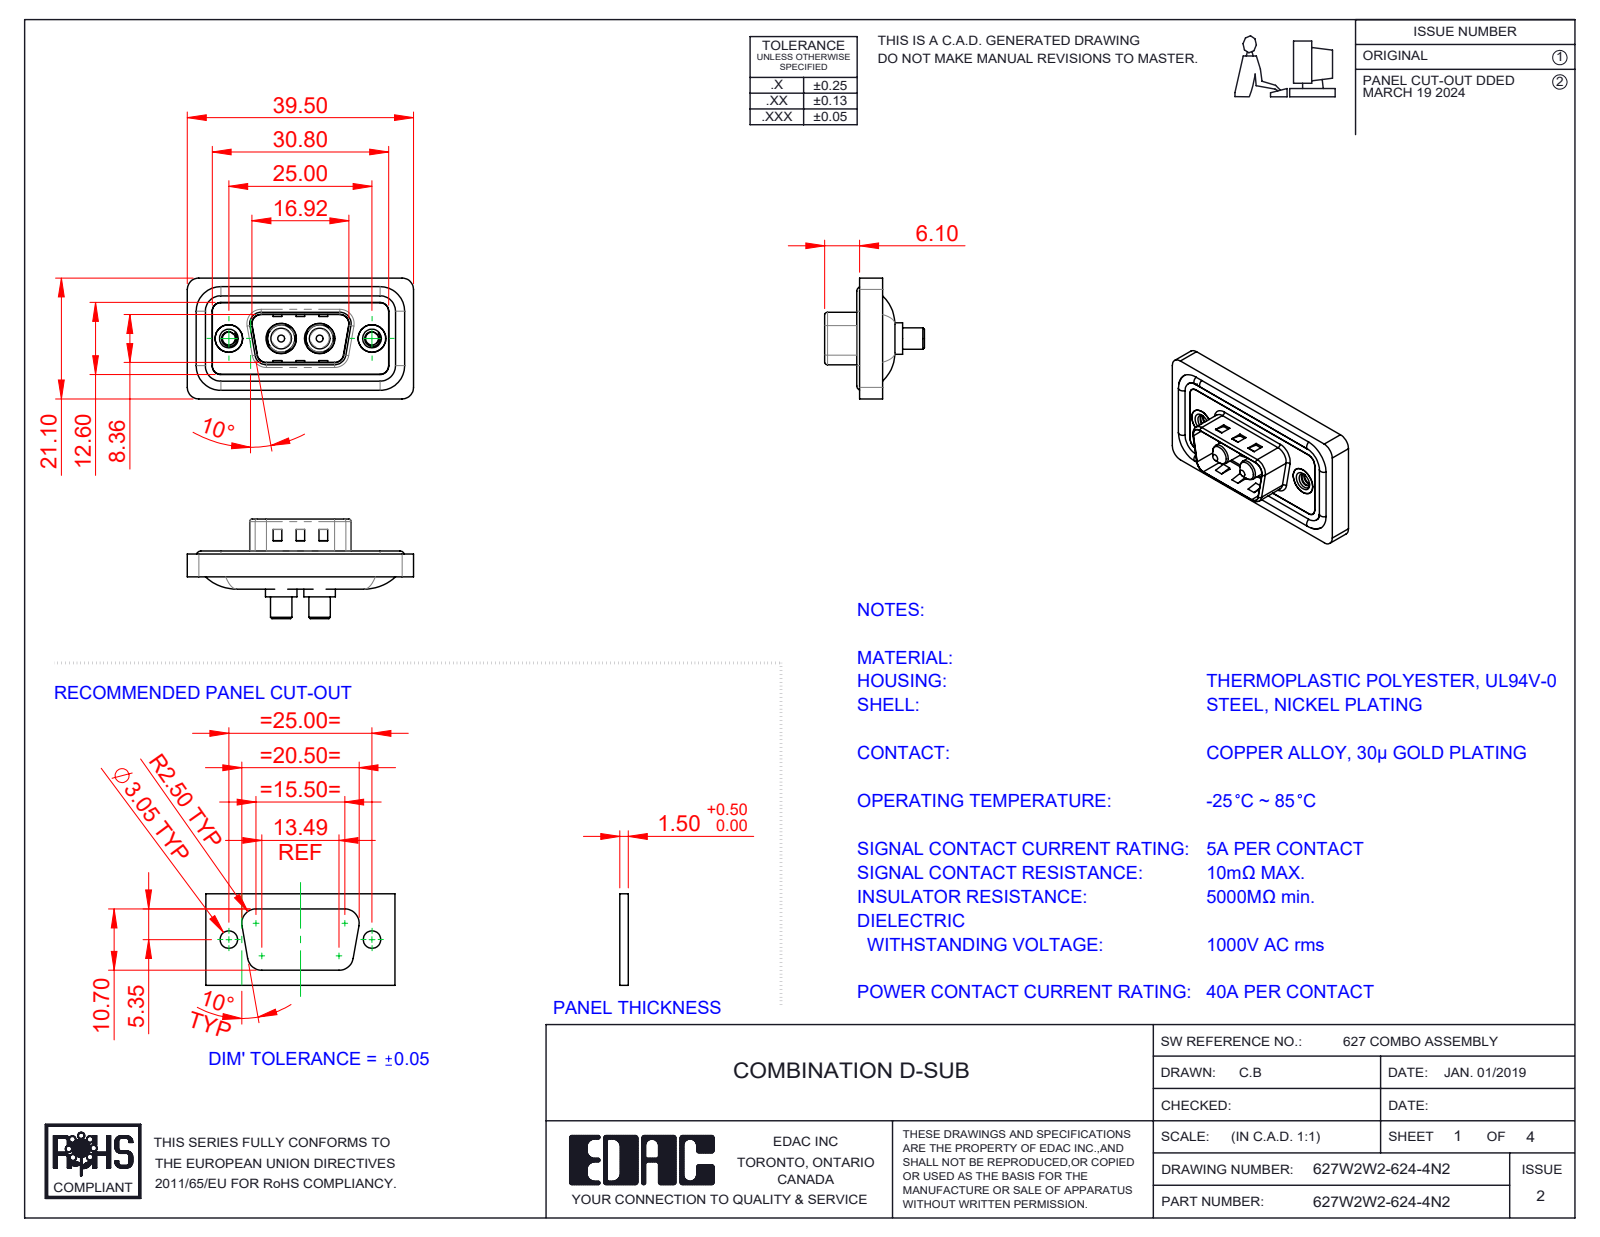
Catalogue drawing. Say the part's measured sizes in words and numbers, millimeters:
The part is named "Power Pin_40A S; 627Combo Threaded Rivet_2; 627Combo Waterproof Housing_09 Contacts; 627W2W2-624-4N2 (+3 more)". Its 3-D file was written by "SolidWorks 2023 (CONFIG_CONTROL_DESIGN)". It is 11 solids with 489 faces: 165 planar, 218 cylindrical and 106 other. Overall it measures 39.5 by 21.1 by 17.4 millimeters. Its volume is 4 497 cubic millimeters and its surface area 7 006 square millimeters. Round holes: 2 of diameter 2.26, 2 of diameter 4, 2 of diameter 4.8, 2 of diameter 4.85, 2 of diameter 5, 2 of diameter 5.3. Round bosses or shafts: 4 of diameter 1.6, 2 of diameter 5.5, 2 of diameter 5.2, 2 of diameter 4.9, 2 of diameter 4.75, 2 of diameter 3.75, 2 of diameter 3.6. Partial cylindrical surfaces (rounded edges, fillets, slot ends): 22 of radius 1.5, 18 of radius 2, 8 of radius 0.5, 8 of radius 1.6, 4 of radius 0.25, 4 of radius 0.6, 4 of radius 0.65, 4 of radius 0.9. The main face-to-face distances are 0.4, 1.1, 2.9, 3.1, 0.5, 1.6, 1.5, 2.5, 4, 0.7. The hole center spacings are 9.14, 15.86, 6.72, 25.
